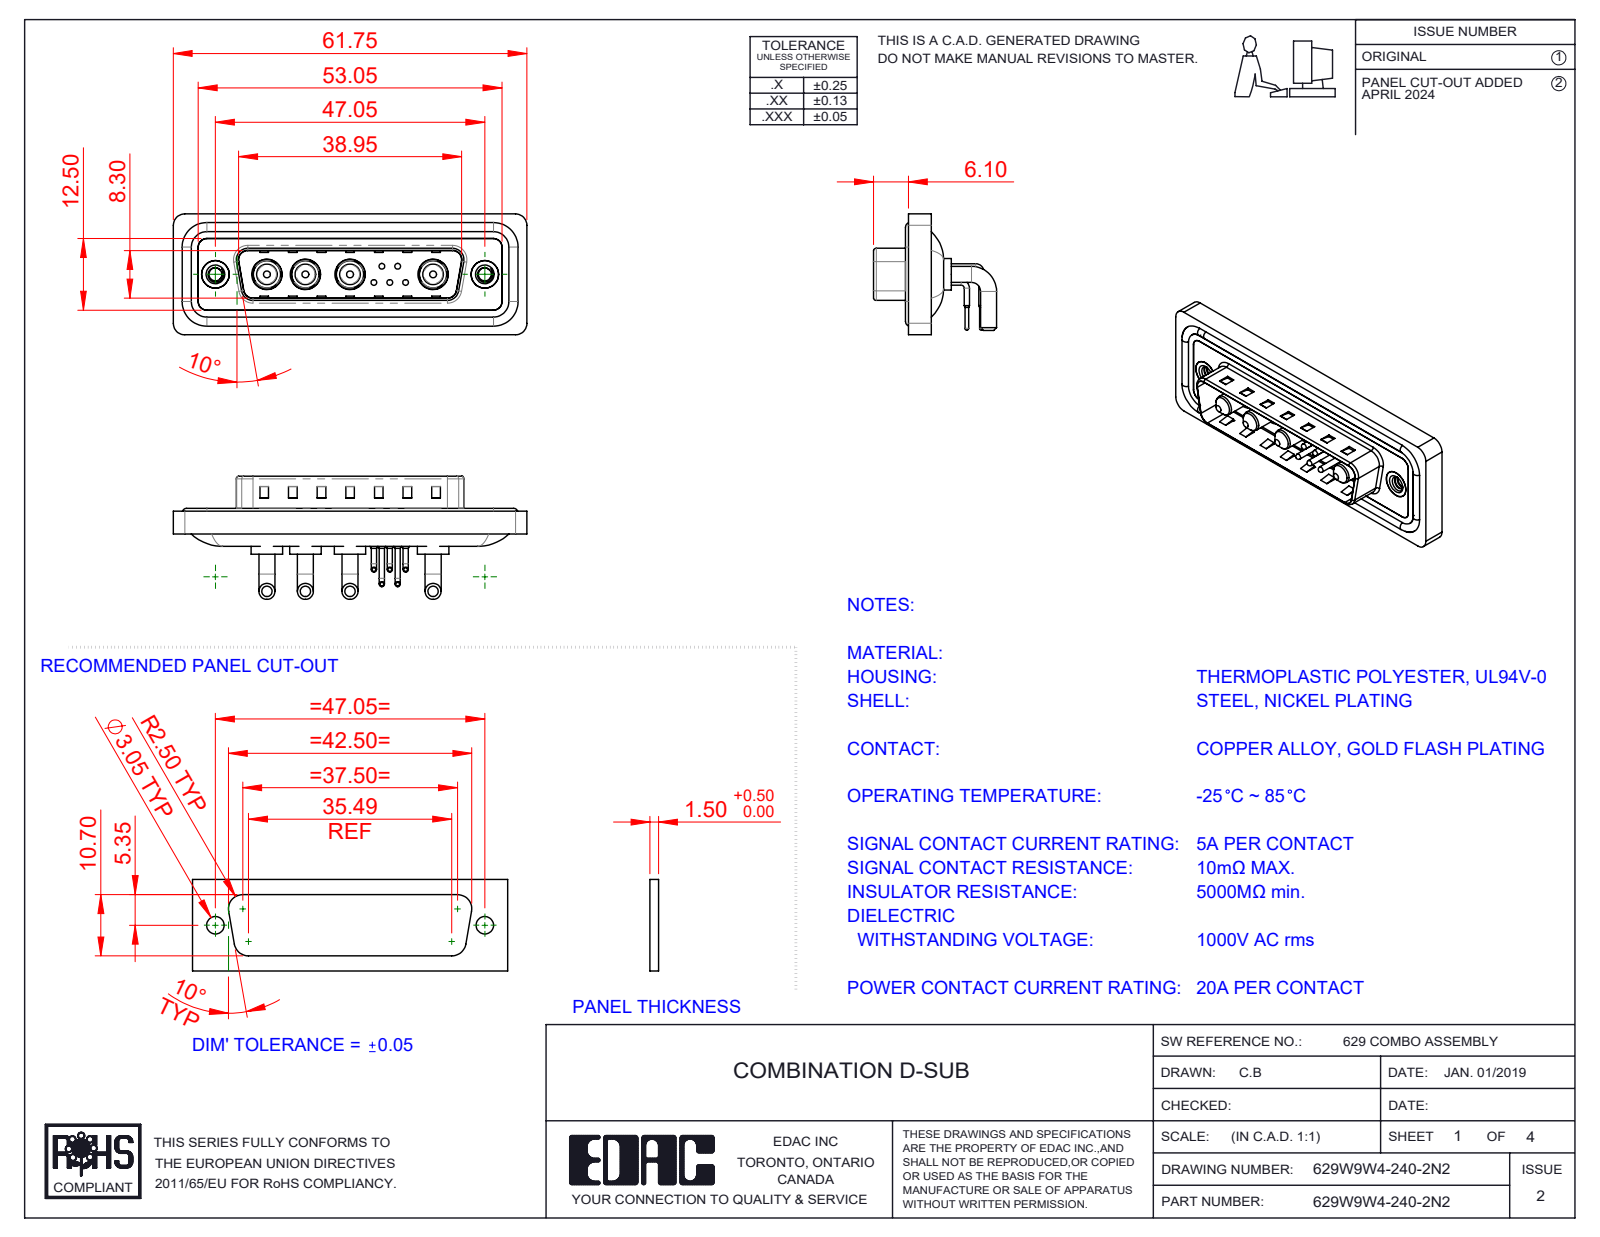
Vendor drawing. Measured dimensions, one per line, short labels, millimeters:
name: 629Combo Threaded Rivet_2; 629Combo Shell Rear_25 Contacts; 629Combo Contact Row 1; 629Combo Contact Row 2 (+5 more)
written by: SolidWorks 2023 (CONFIG_CONTROL_DESIGN)
unit: mm
bodies: 20 solids, 1205 faces (569 planar, 452 cylindrical, 184 other)
size: 61.75 × 21.5 × 21.1
volume: 7 715 mm³; area: 12 377 mm²
holes: 5× ⌀0.75, 5× ⌀1.6, 5× ⌀2, 4× ⌀4.85, 4× ⌀5.3, 2× ⌀2.26, 2× ⌀4, 2× ⌀4.8, 2× ⌀5
bosses: 10× ⌀0.9, 8× ⌀2.8, 5× ⌀1.5, 5× ⌀1, 5× ⌀0.65, 4× ⌀5.5, 4× ⌀5.2, 4× ⌀4.75
rounds: 18× R1.5, 18× R2, 8× R0.5, 8× R1.6, 5× R1.01, 4× R0.25, 4× R0.6, 4× R0.65
face distances: 0.4, 2.9, 0.8, 4.1, 1.1, 4.5, 2.1, 1.6, 1.5, 3.1
hole spacings: 3.16, 2.77, 5.04, 14.5, 2.78, 4.4, 4.41, 5
